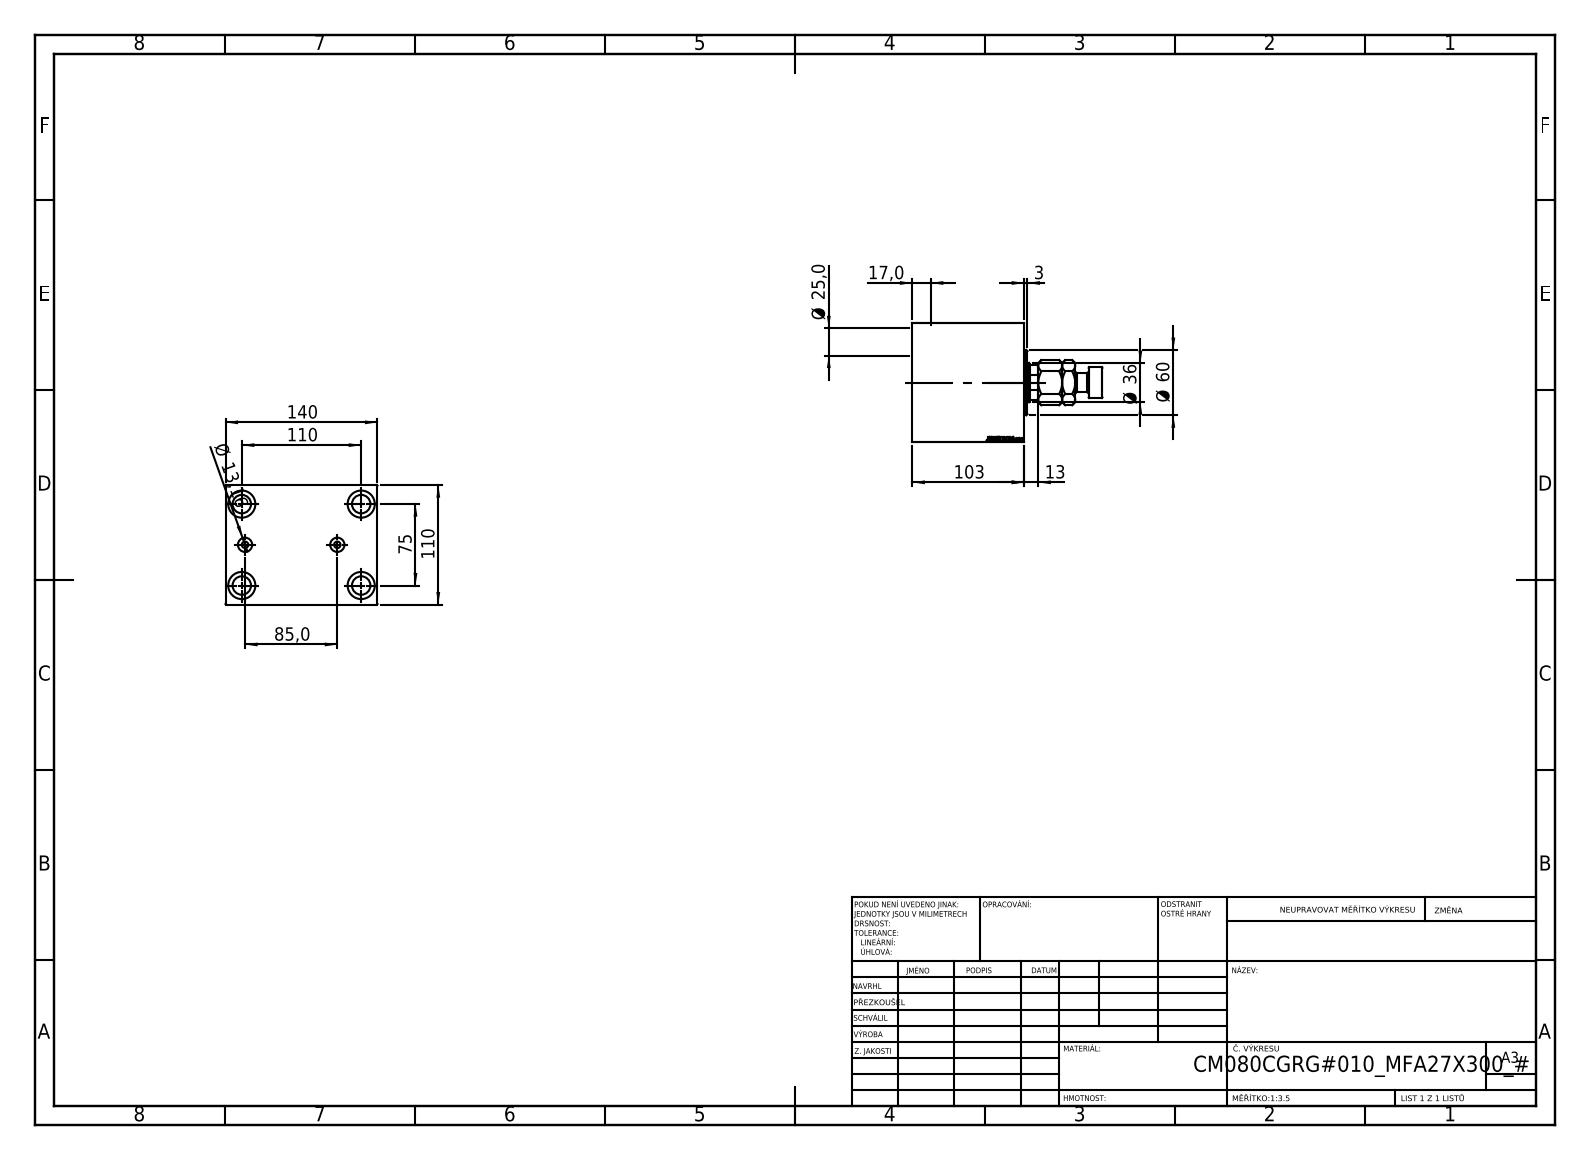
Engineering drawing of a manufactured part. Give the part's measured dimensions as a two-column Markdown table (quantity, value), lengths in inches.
| quantity | value |
| --- | --- |
| part name | V450CM_C_Body; MFA; V450CM_C_VCP; V450CM_VC_B |
| STEP written by | SolidWorks 2019 (CONFIG_CONTROL_DESIGN) |
| units | inches |
| bodies | 4 solids, 912 faces (424 planar, 62 cylindrical, 426 other) |
| overall size | 6.89 × 5.512 × 4.331 |
| volume | 89.03 in³ |
| surface area | 266.8 in² |
| round holes (diameter × count) | 0.669 × 4, 0.984 × 4, 0.236 × 2, 0.518 × 2, 1.004 × 1, 1.417 × 1, 1.555 × 1, 3.15 × 1, 3.228 × 1, 3.425 × 1 |
| round bosses / shafts (diameter × count) | 2.362 × 1, 1.102 × 1, 0.709 × 1 |
| partial cylindrical surfaces (radius × count) | 0.689 × 1 |
| main face-to-face distances | 4.331, 2.047, 5.512, 4.055, 2.008, 0.394, 0.85, 1.157, 3.205, 2.811 |
| hole center spacings | 2.621, 1.481, 1.712, 2.953, 3.766, 4.331, 4.464, 5.242 |
